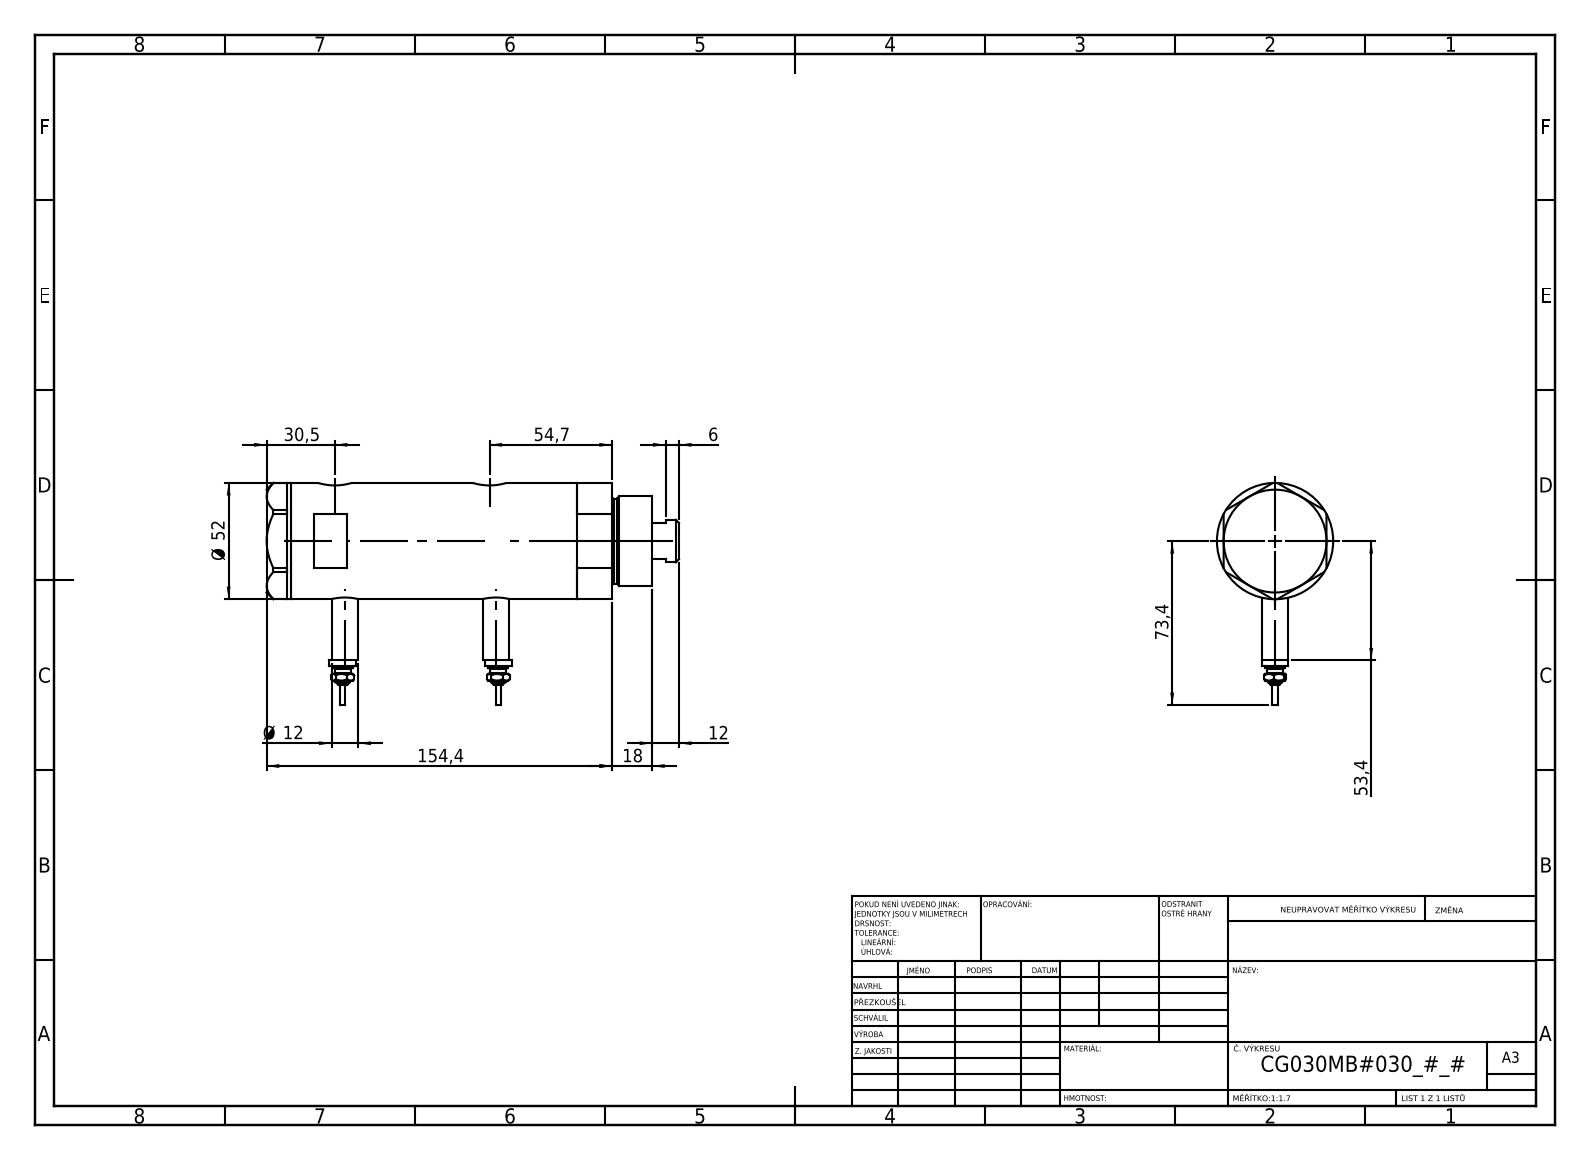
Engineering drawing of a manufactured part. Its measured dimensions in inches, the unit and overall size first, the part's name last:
Units: inches
Overall size (bounding box): 7.26 × 3.913 × 2.047
Round holes (diameter × count): ⌀0.383 ×2, ⌀0.492 ×2, ⌀0.591 ×2, ⌀0.256 ×1, ⌀0.787 ×1, ⌀0.846 ×1, ⌀1.181 ×1, ⌀1.299 ×1, ⌀1.732 ×1
Round bosses / shafts (diameter × count): ⌀0.472 ×4, ⌀0.354 ×2, ⌀0.276 ×2, ⌀0.177 ×2, ⌀0.098 ×2, ⌀2.047 ×1, ⌀1.575 ×1, ⌀1.496 ×1
Main face-to-face distances: 3.602, 0.937, 2.665, 0.433, 1.37, 4.035, 1.811, 1.433, 5.469, 5.035
Hole centre spacings: 0.114, 0.177, 2.547, 2.661, 2.724, 2.839
Volume: 20.81 in³ · Surface area: 123.9 in²
Bodies: 6 solids, 226 faces (93 planar, 69 cylindrical, 64 other)
Part name (STEP PRODUCT): V270CG_BACK; V270CG_FRONT; V270CG_VC; Switch (+1 more)
STEP written by: SolidWorks 2019 (CONFIG_CONTROL_DESIGN)
